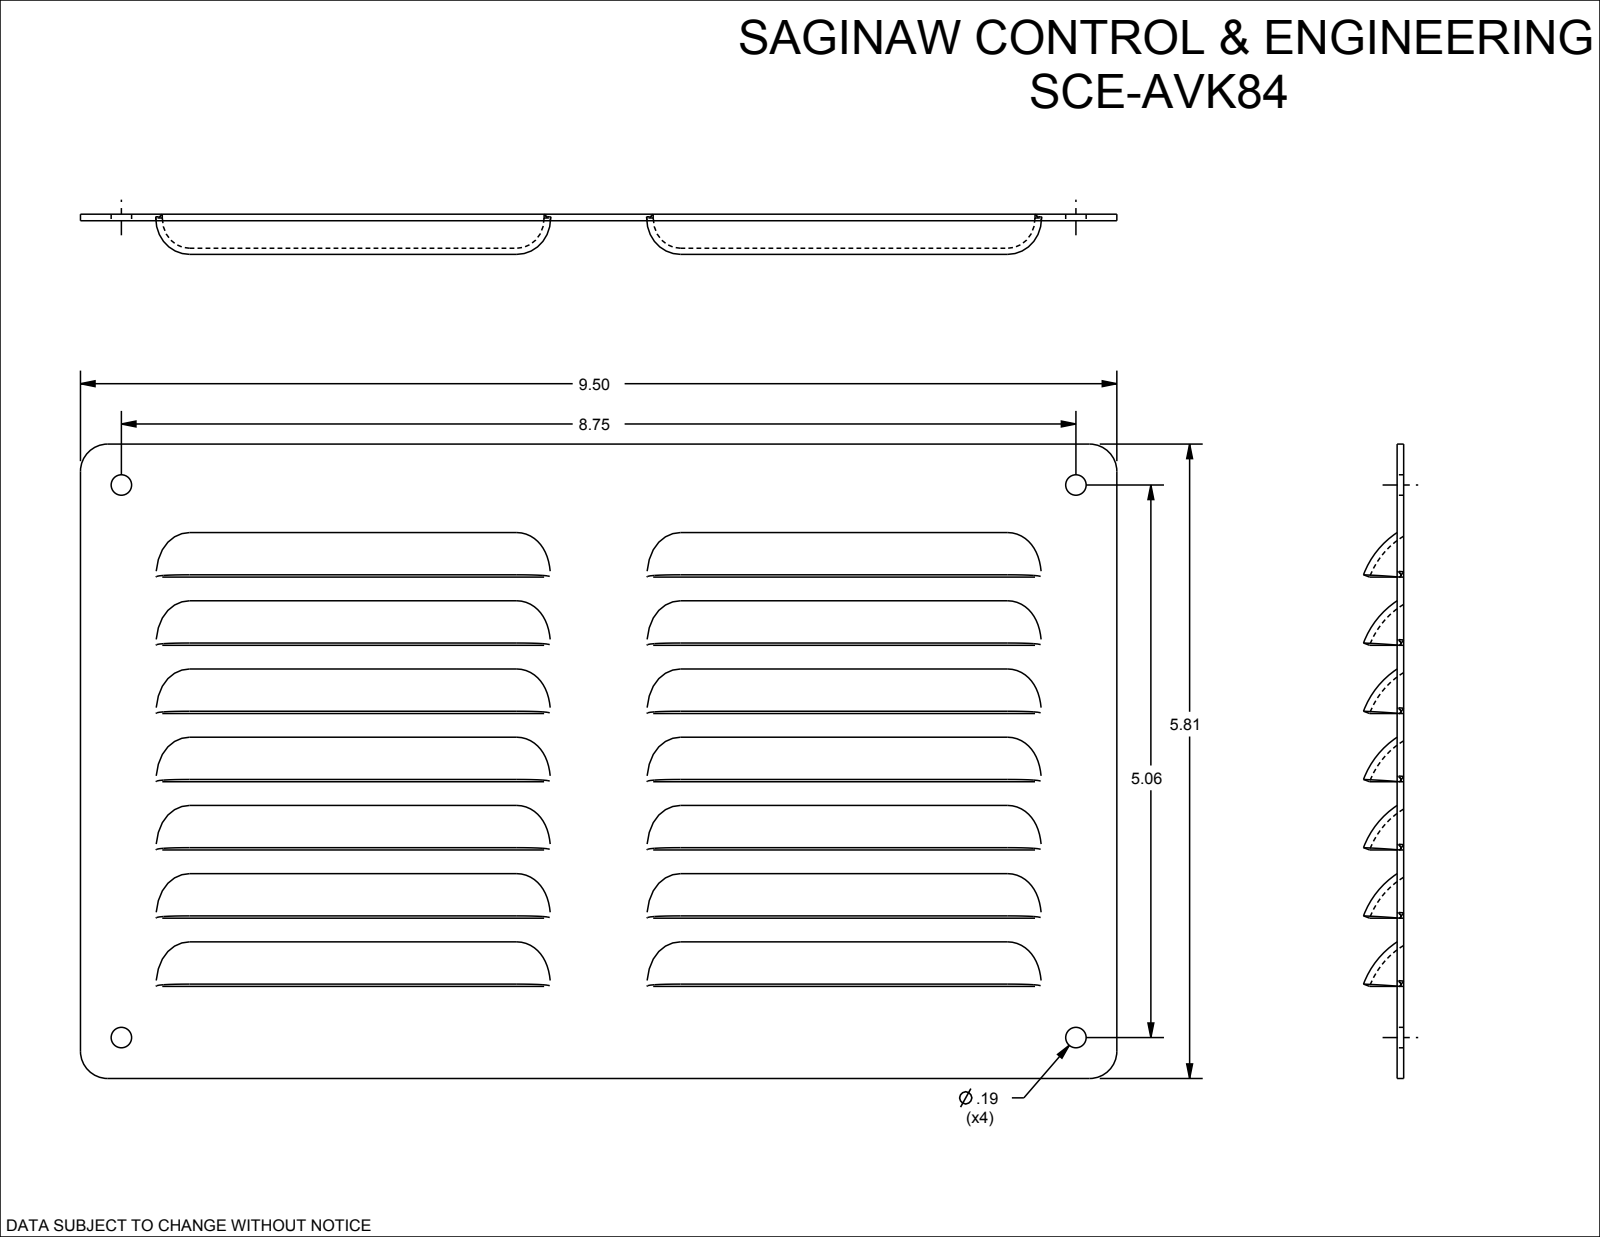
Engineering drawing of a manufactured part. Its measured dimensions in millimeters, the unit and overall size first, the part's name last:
Units: millimetres
Overall size (bounding box): 241.3 × 147.7 × 11.9
Round holes (diameter × count): ⌀4.7 ×4
Partial cylindrical surfaces — rounded edges, fillets, slot ends (radius × count): R18.8 ×7, R20.3 ×7, R6.4 ×4
Main face-to-face distances: 1.5, 31.8, 15.9, 63.5, 15.9, 7.4, 24.4, 29.7, 47.6, 47.6
Hole centre spacings: 128.6, 222.3, 256.8
Volume: 61 210 mm³ · Surface area: 85 100 mm²
Bodies: 1 solid, 228 faces (48 planar, 68 cylindrical, 112 other)
Part name (STEP PRODUCT): SCE-AVK84
STEP written by: SolidWorks 2021 (AUTOMOTIVE_DESIGN)
